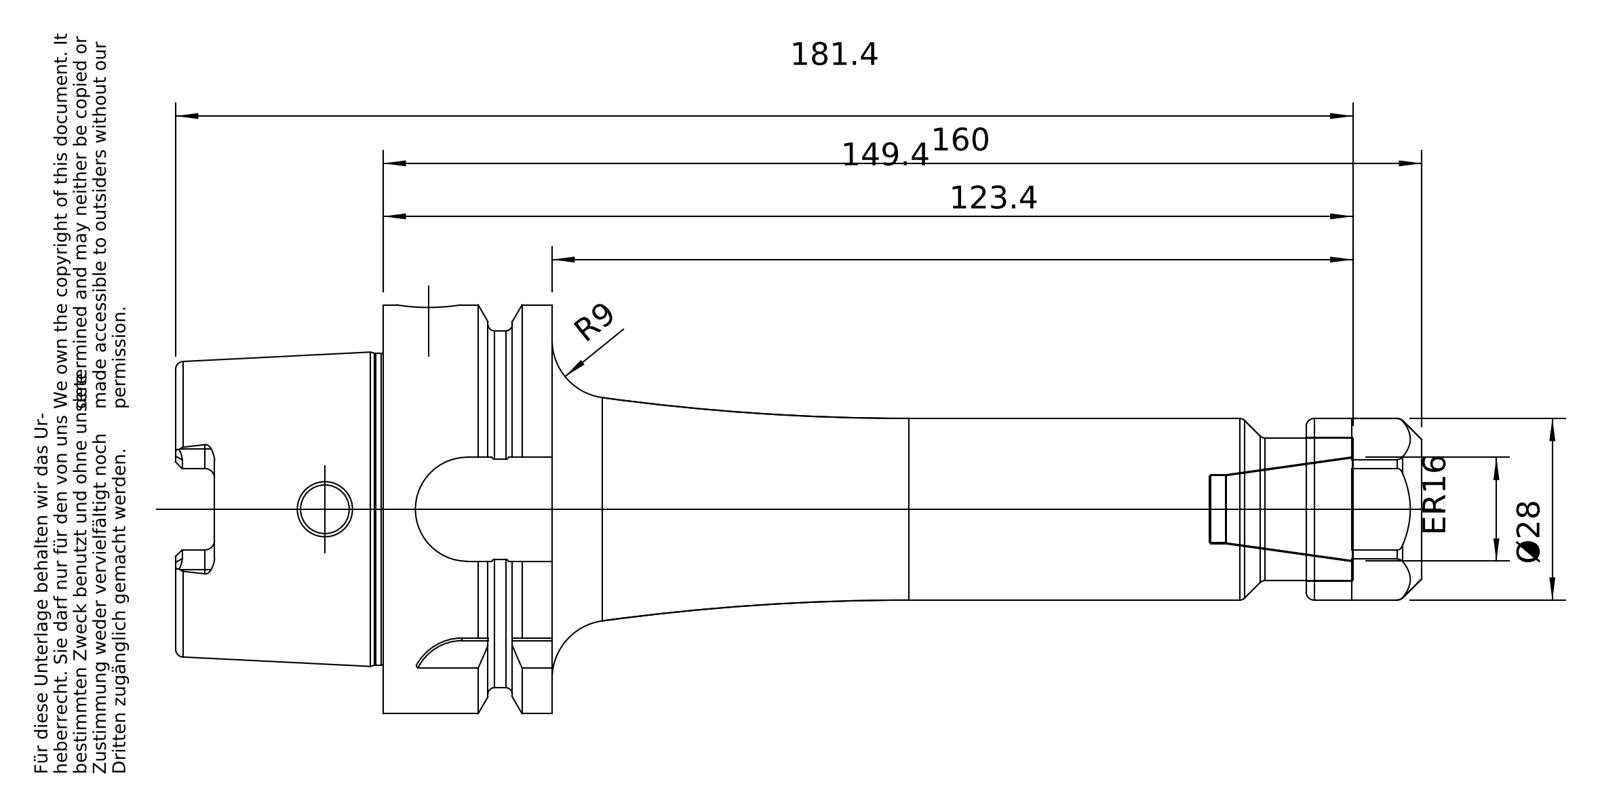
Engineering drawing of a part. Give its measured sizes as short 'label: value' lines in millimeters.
name: A63-022-16; 83-912-16; A63-022-16_ASM
written by: PRO/ENGINEER BY PARAMETRIC TECHNOLOGY CORPORATION, 2010430 (CONFIG_CONTROL_DESIGN)
unit: mm
bodies: 2 solids, 207 faces (65 planar, 52 cylindrical, 90 other)
size: 192 × 63 × 63
volume: 170 169 mm³; area: 36 157 mm²
holes: 1× ⌀7.5, 1× ⌀10, 1× ⌀10.5, 1× ⌀16.92, 1× ⌀18.32, 1× ⌀18.66, 1× ⌀34, 1× ⌀40
bosses: 1× ⌀63, 1× ⌀55, 1× ⌀48.04, 1× ⌀28, 1× ⌀22, 1× ⌀18
rounds: 6× R1.5, 4× R3, 1× R8, 1× R8.02, 1× R9.02
face distances: 26, 10, 142.2, 116.2, 16, 132.2, 32, 25, 42, 58
